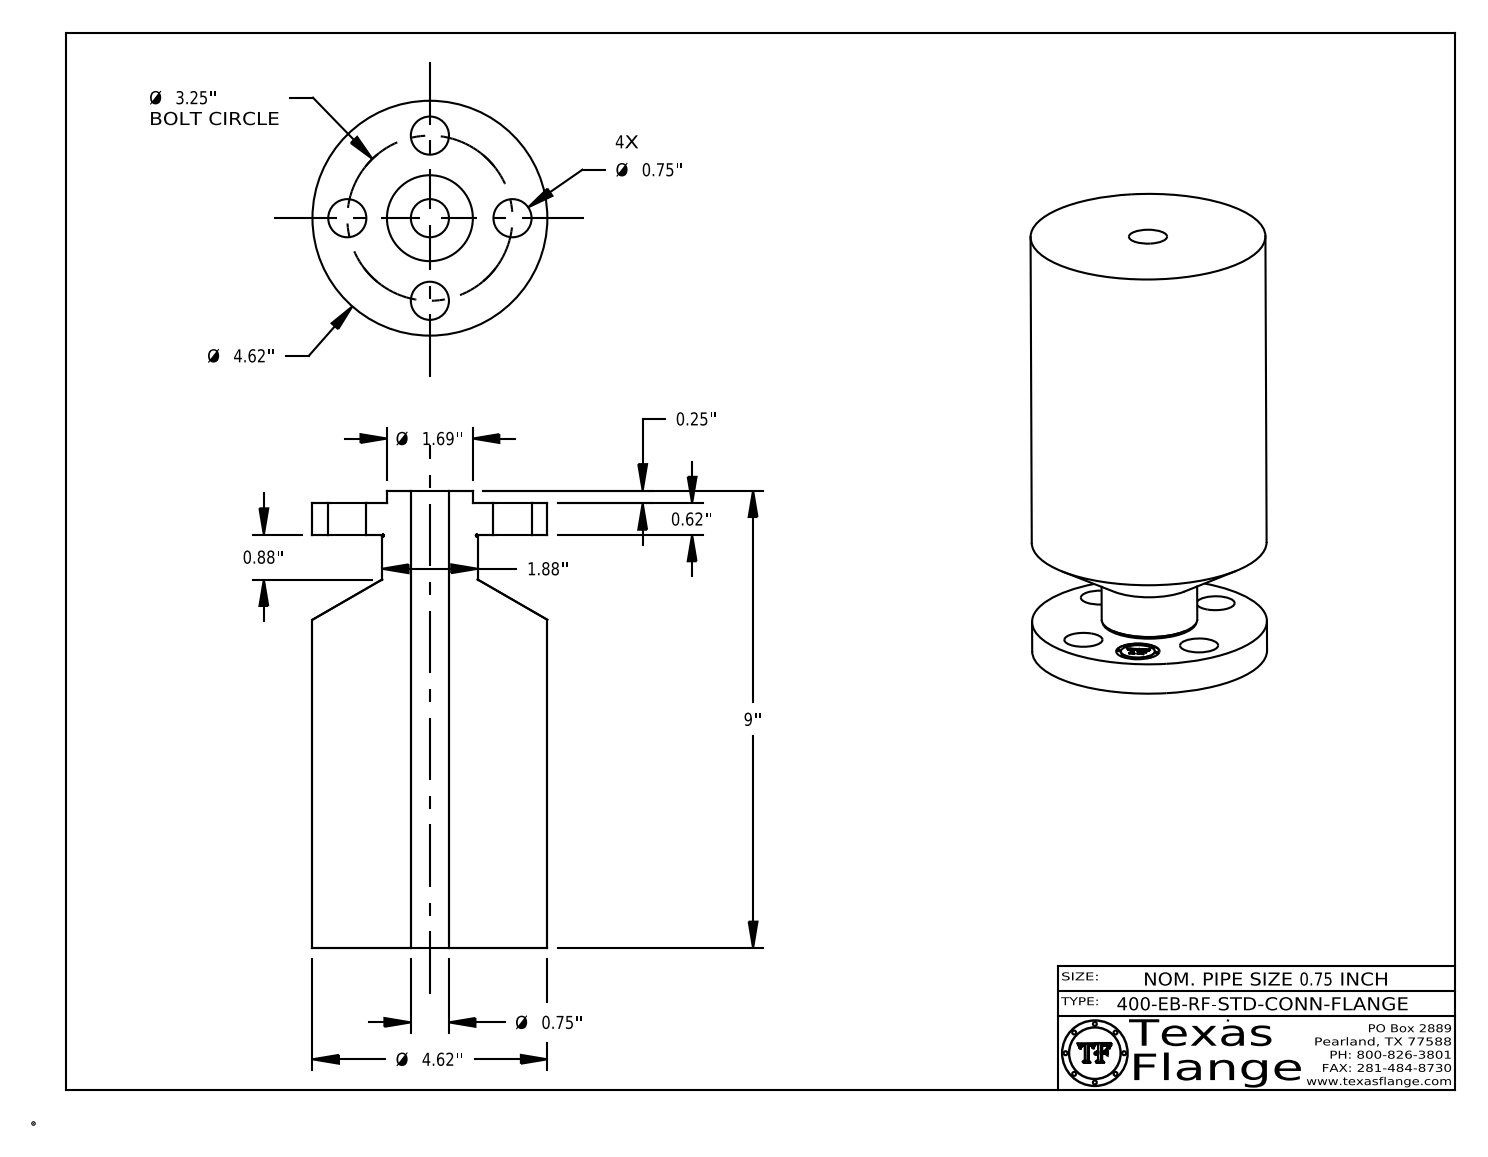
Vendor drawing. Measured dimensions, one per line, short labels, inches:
name: 0.75-400-EB-RF-STD-CONN-FLANGE
written by: CATIA V5 STEP AP214 (AUTOMOTIVE_DESIGN)
unit: in
bodies: 1 solid, 413 faces (369 planar, 38 cylindrical, 6 other)
size: 9 × 4.62 × 4.62
volume: 123.5 in³; area: 195.8 in²
holes: 5× ⌀0.75, 1× ⌀0.85
bosses: 8× ⌀0.051, 1× ⌀4.62, 1× ⌀1.88, 1× ⌀1.69, 1× ⌀0.67
face distances: 8.75, 0.62, 8.13, 0.25, 0.87, 9, 0.865, 0.615, 8.135, 0.254
hole spacings: 1.625, 2.298, 1.244, 3.003, 3.25
